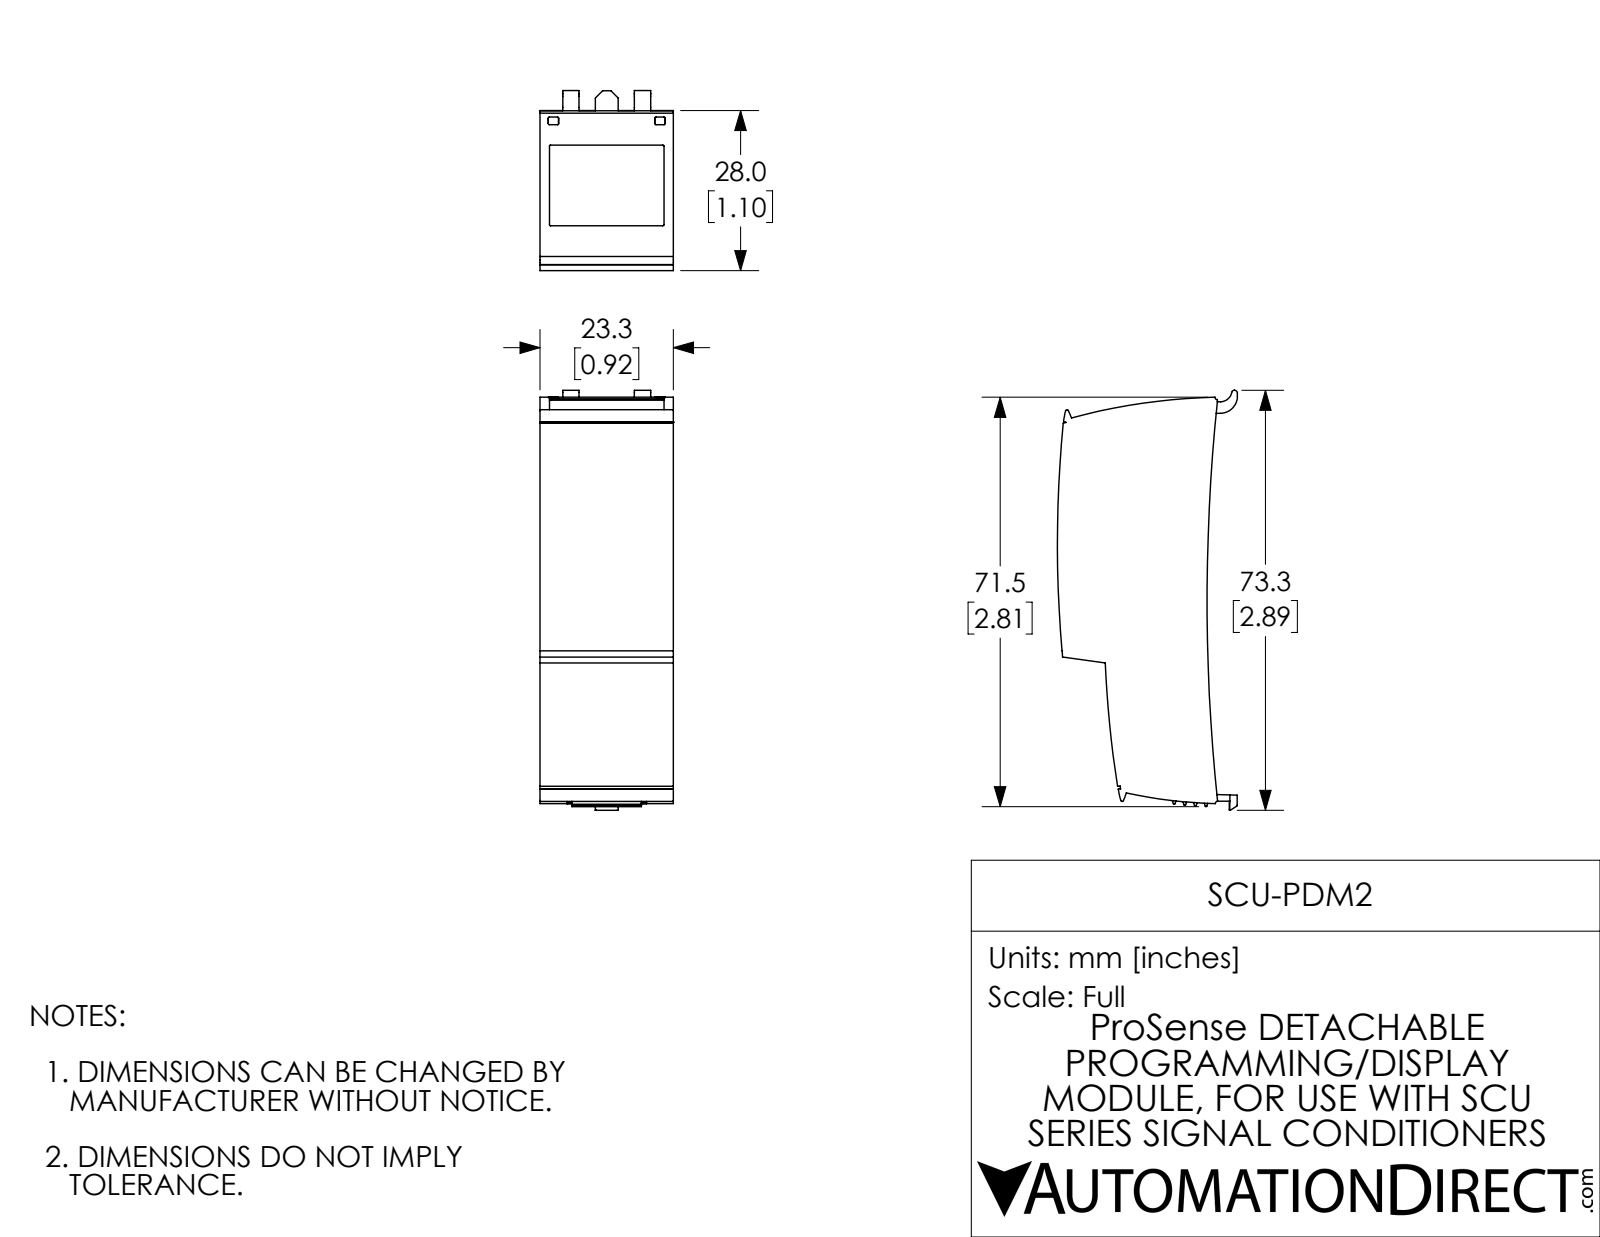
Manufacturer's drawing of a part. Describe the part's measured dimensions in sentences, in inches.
The part is named "SCU-PDM2 mod1". Its 3-D file was written by "SolidWorks 2017 (AUTOMOTIVE_DESIGN)". It is 1 solid with 141 faces: 56 planar, 57 cylindrical and 28 other. Overall it measures 2.886 by 1.238 by 0.917 inches. Its volume is 2.27 cubic inches and its surface area 12.24 square inches. Partial cylindrical surfaces (rounded edges, fillets, slot ends): 12 of radius 0.591, 4 of radius 0.005, 4 of radius 0.006, 2 of radius 0.01, 2 of radius 0.018, 2 of radius 4.134, 1 of radius 0.016, 1 of radius 0.02. The main face-to-face distances are 0.917, 0.157, 0.761, 0.269, 0.649, 0.112, 0.492, 0.189, 0.729, 0.032.
